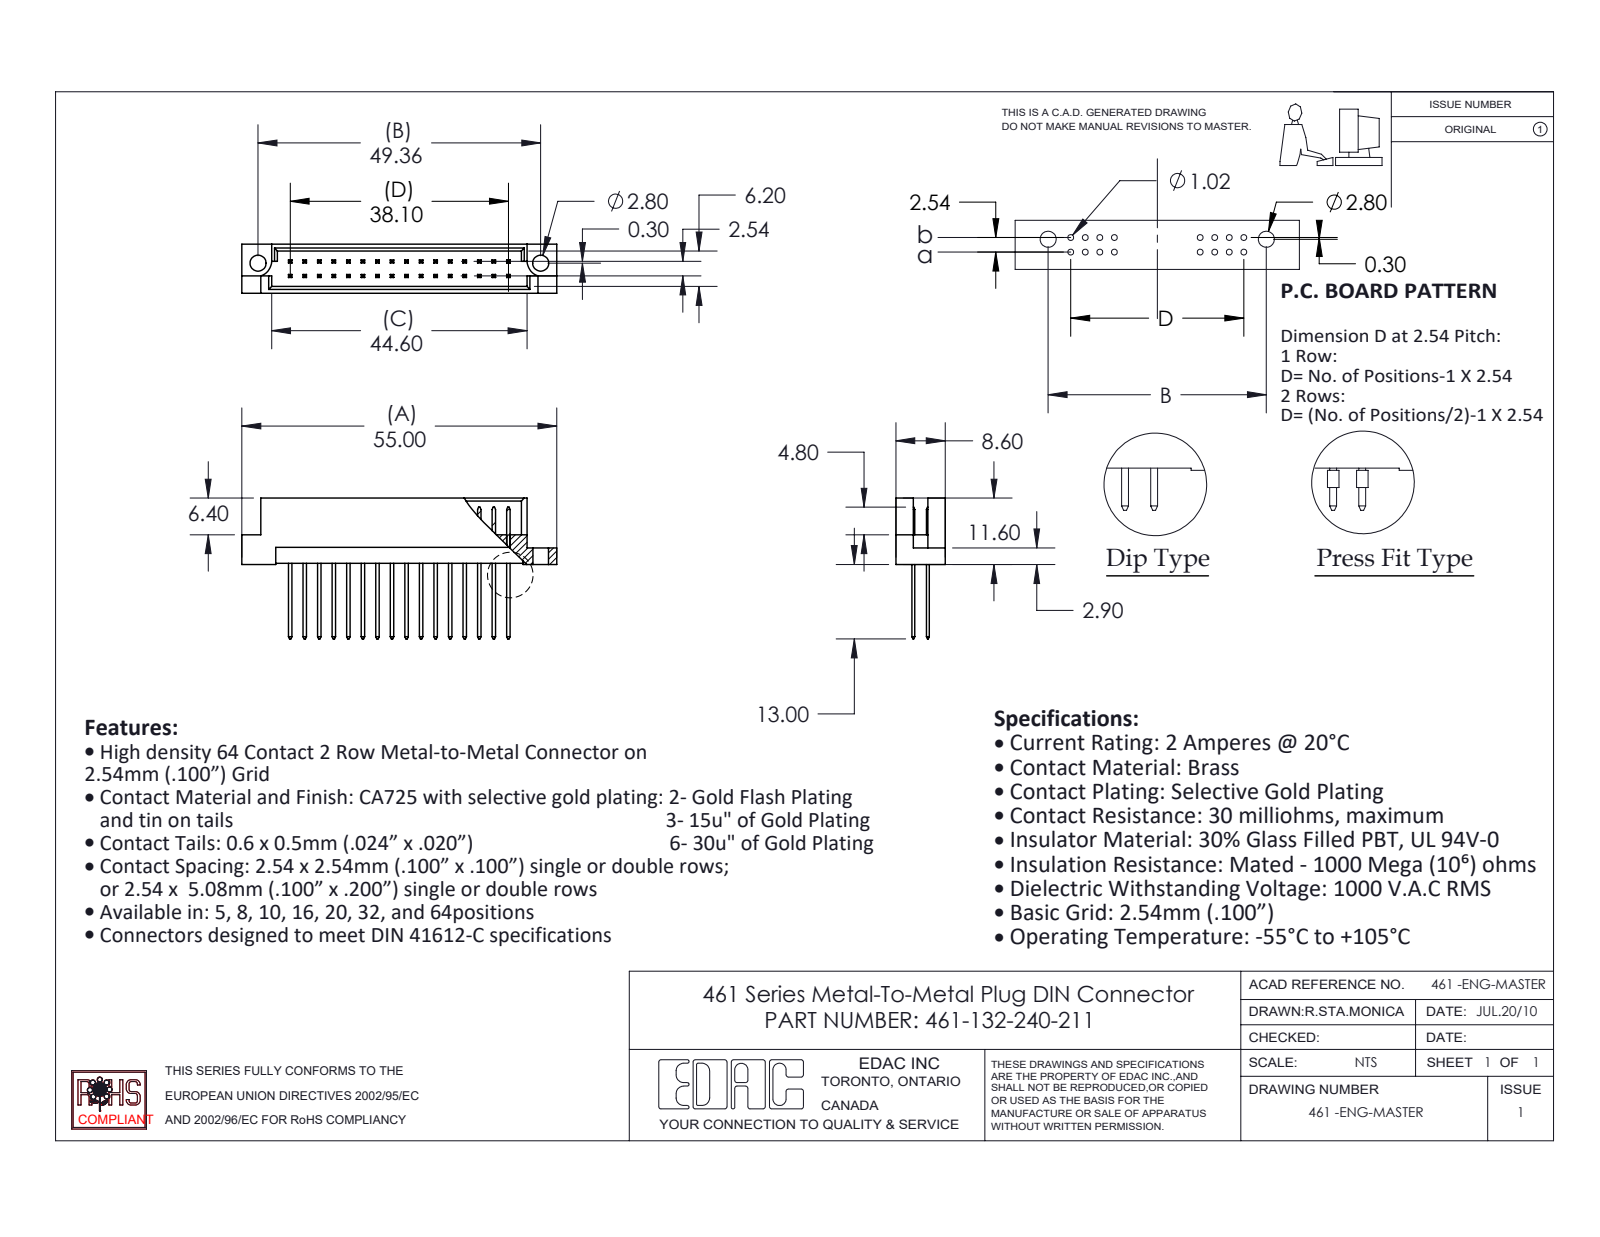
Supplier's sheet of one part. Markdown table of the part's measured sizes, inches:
| quantity | value |
| --- | --- |
| part name | 461-290_40; 461 Part_32; 461-132-240-211 |
| STEP written by | SolidWorks 2020 (CONFIG_CONTROL_DESIGN) |
| units | inches |
| bodies | 33 solids, 624 faces (618 planar, 6 cylindrical, 0 other) |
| overall size | 2.165 × 0.969 × 0.339 |
| volume | 0.175 in³ |
| surface area | 7.524 in² |
| round holes (diameter × count) | 0.11 × 2 |
| partial cylindrical surfaces (radius × count) | 0.11 × 2 |
| main face-to-face distances | 0.1, 0.047, 0.291, 0.109, 0.229, 0.062, 0.182, 0.129, 0.209, 0.082 |
| hole center spacings | 1.943 |
